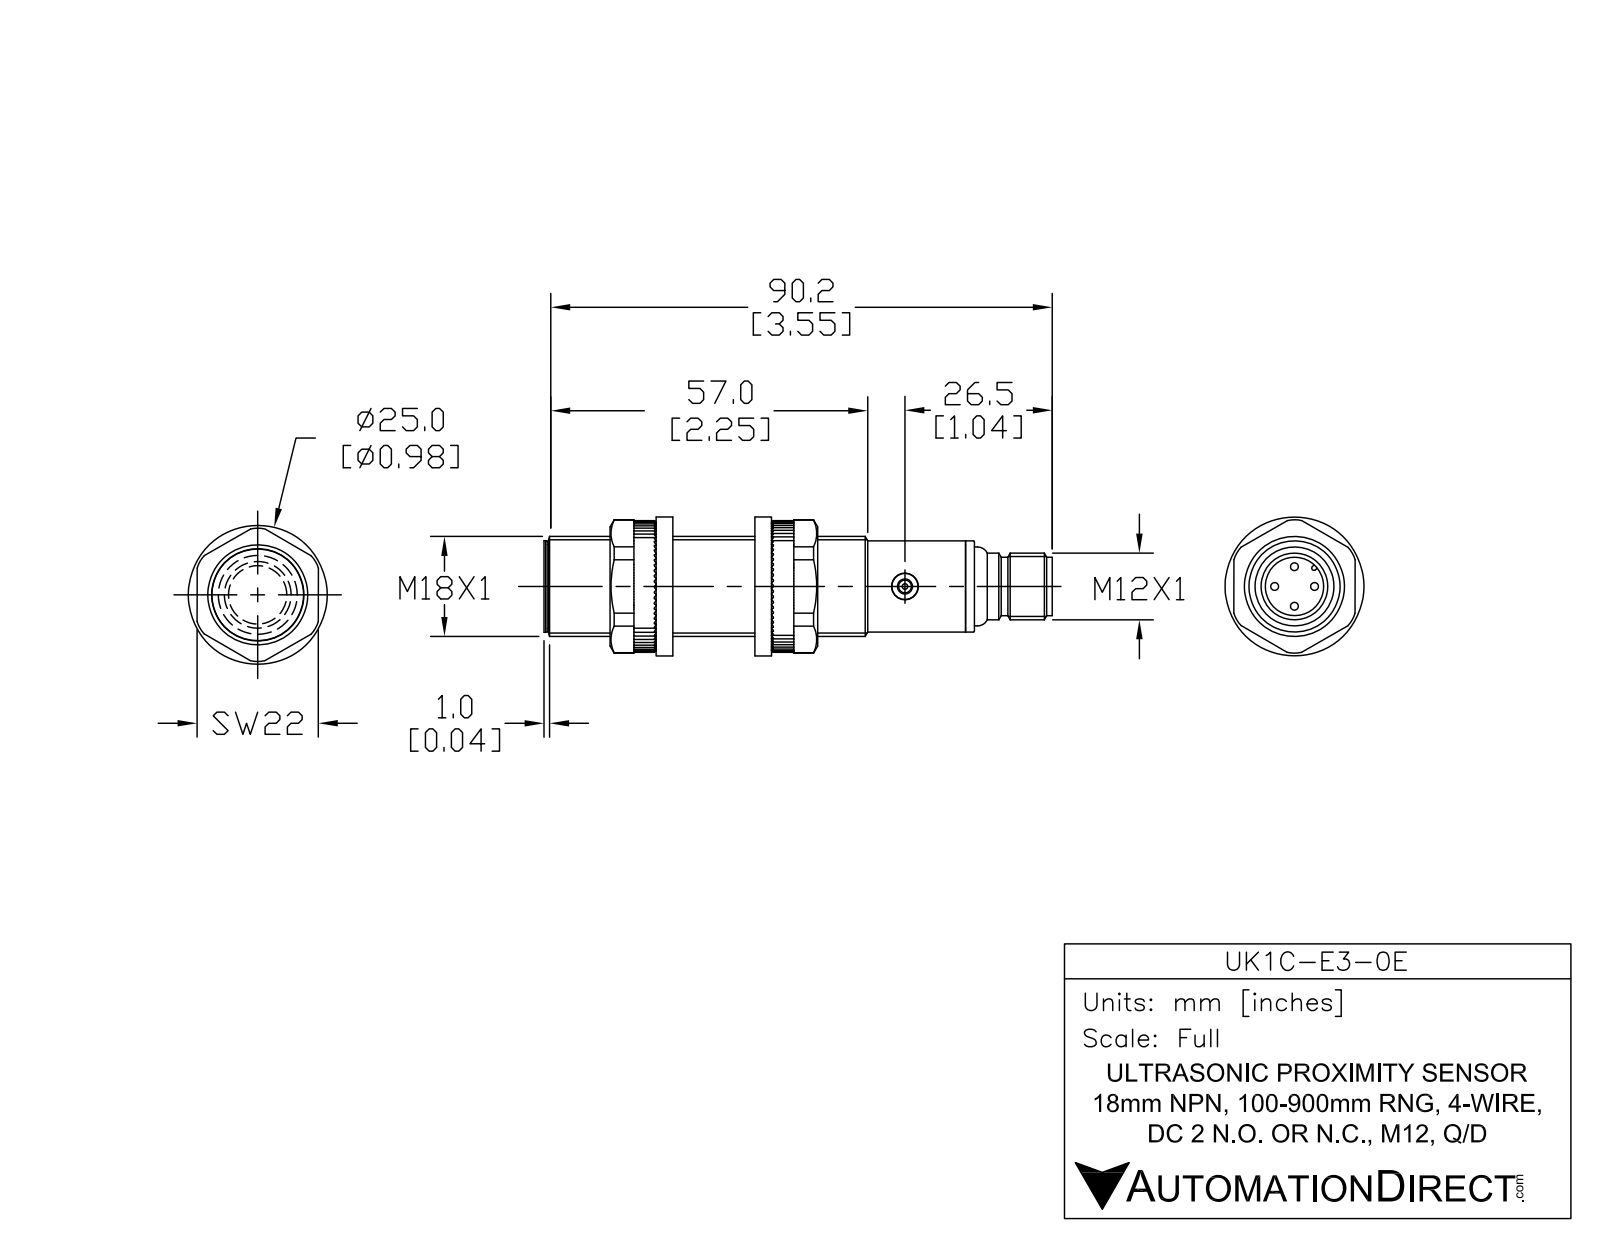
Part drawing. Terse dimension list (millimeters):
name: UK1C-E3-0E
written by: SolidWorks 2017 (AUTOMOTIVE_DESIGN)
unit: mm
bodies: 6 solids, 106 faces (21 planar, 48 cylindrical, 37 other)
size: 91.6 × 18 × 18
volume: 19 700 mm³; area: 6 890 mm²
holes: 1× ⌀2.7, 1× ⌀4.7, 1× ⌀7, 1× ⌀8.3, 1× ⌀9.5
bosses: 4× ⌀1, 1× ⌀18, 1× ⌀16.6, 1× ⌀16.4, 1× ⌀15.8, 1× ⌀14.2, 1× ⌀12, 1× ⌀10.5
rounds: 1× R0.6
face distances: 75.1, 1, 76.1, 0.9, 76, 1.1, 4, 77.6, 77.5, 76.6
